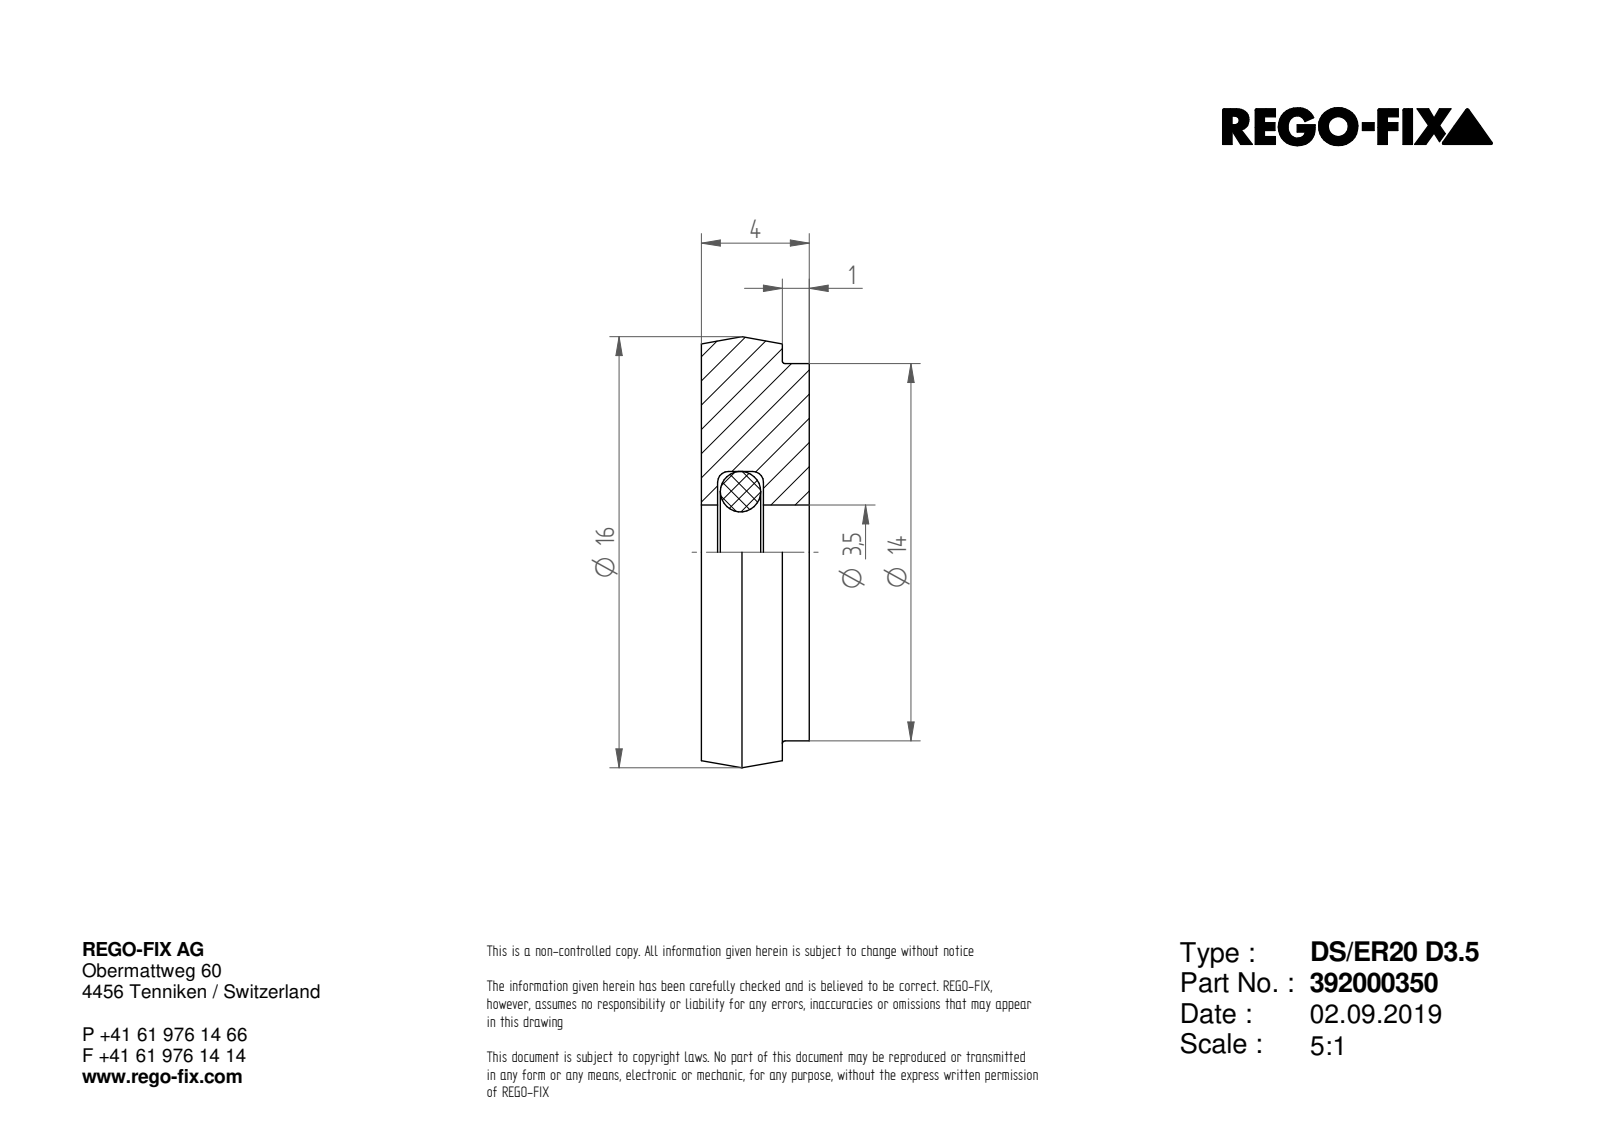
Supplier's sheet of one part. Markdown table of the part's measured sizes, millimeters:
| quantity | value |
| --- | --- |
| part name | NOCUT |
| STEP written by | SIEMENS PLM Software Solid Edge ST10 (AUTOMOTIVE_DESIGN) |
| units | millimeters |
| bodies | 1 solid, 7 faces (3 planar, 3 cylindrical, 1 other) |
| overall size | 16 × 16 × 4 |
| volume | 719 mm³ |
| surface area | 620 mm² |
| round holes (diameter × count) | 3.5 × 1 |
| round bosses / shafts (diameter × count) | 16 × 1, 14 × 1 |
| main face-to-face distances | 4, 1, 3 |
